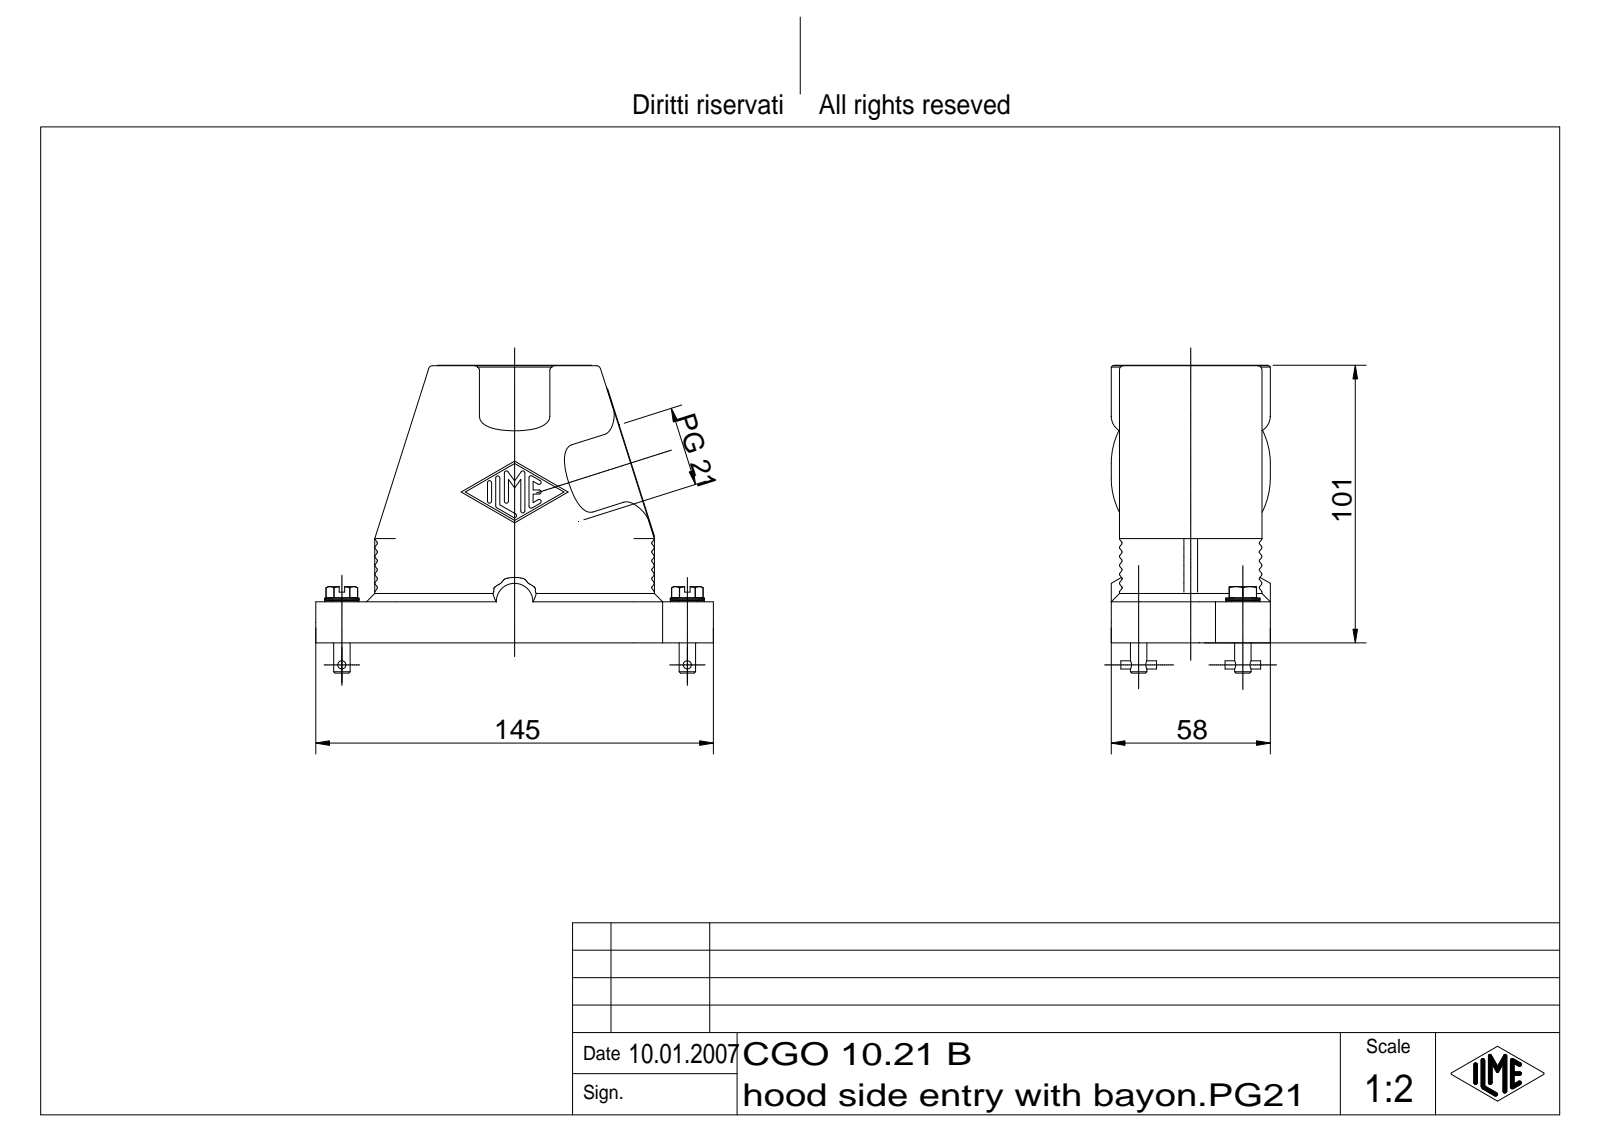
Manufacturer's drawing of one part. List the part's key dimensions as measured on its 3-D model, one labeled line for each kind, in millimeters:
Part name (STEP PRODUCT): CGO 10.21 B
STEP written by: Autodesk Inventor 7 (AUTOMOTIVE_DESIGN)
Units: millimetres
Bodies: 3 solids, 793 faces (198 planar, 211 cylindrical, 384 other)
Overall size (bounding box): 145 × 112.2 × 58
Volume: 207 080 mm³ · Surface area: 72 922 mm²
Round holes (diameter × count): ⌀2.46 ×2, ⌀3.2 ×2, ⌀6.6 ×2, ⌀15 ×2, ⌀26.78 ×1
Round bosses / shafts (diameter × count): ⌀56 ×2, ⌀12.5 ×2, ⌀6 ×2, ⌀3 ×2, ⌀58 ×1
Partial cylindrical surfaces — rounded edges, fillets, slot ends (radius × count): R0.5 ×39, R0.75 ×14, R7.5 ×8, R6 ×6, R1.5 ×4, R3 ×4, R5.75 ×2, R10.5 ×2
Main face-to-face distances: 3, 52, 49, 6, 55, 2.5, 46, 0.5, 58, 3.5
Hole centre spacings: 34.94, 97.1, 63.07, 131.61
